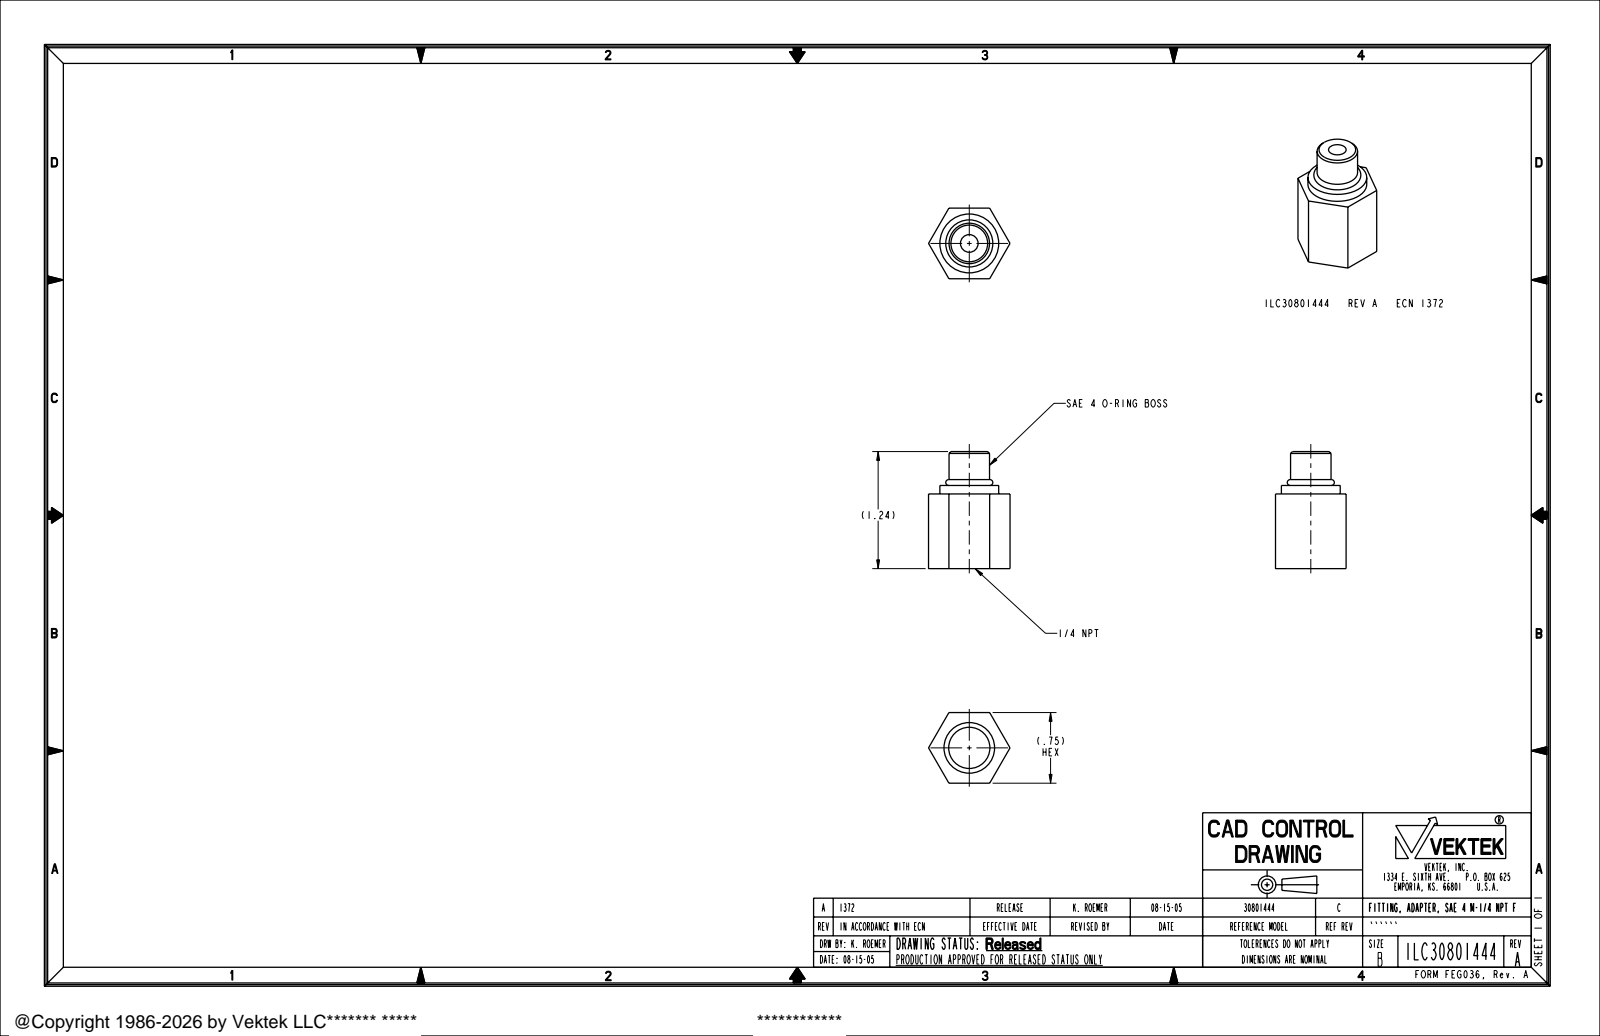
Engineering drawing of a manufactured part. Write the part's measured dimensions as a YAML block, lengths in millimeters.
part_name: "ILC30801444"
step_written_by: "PRO/ENGINEER BY PARAMETRIC TECHNOLOGY CORPORATION, 2004290 (AUTOMOTIVE_DESIGN_CC2)"
units: millimeters
bodies: {solids: 1, faces: 28, planar: 12, cylindrical: 10, other: 6}
overall_size: [31.6, 22, 19.1]
volume: 5950
surface_area: 3121
round_holes:
  - {diameter: 4.7, count: 1}
  - {diameter: 11.1, count: 1}
round_bosses_or_shafts:
  - {diameter: 15.9, count: 1}
  - {diameter: 10.9, count: 1}
face_to_face_distances: [19.1, 20.1, 22.4, 2.3, 15.2, 4.9, 7.2, 31.6, 16.3, 11.4]
